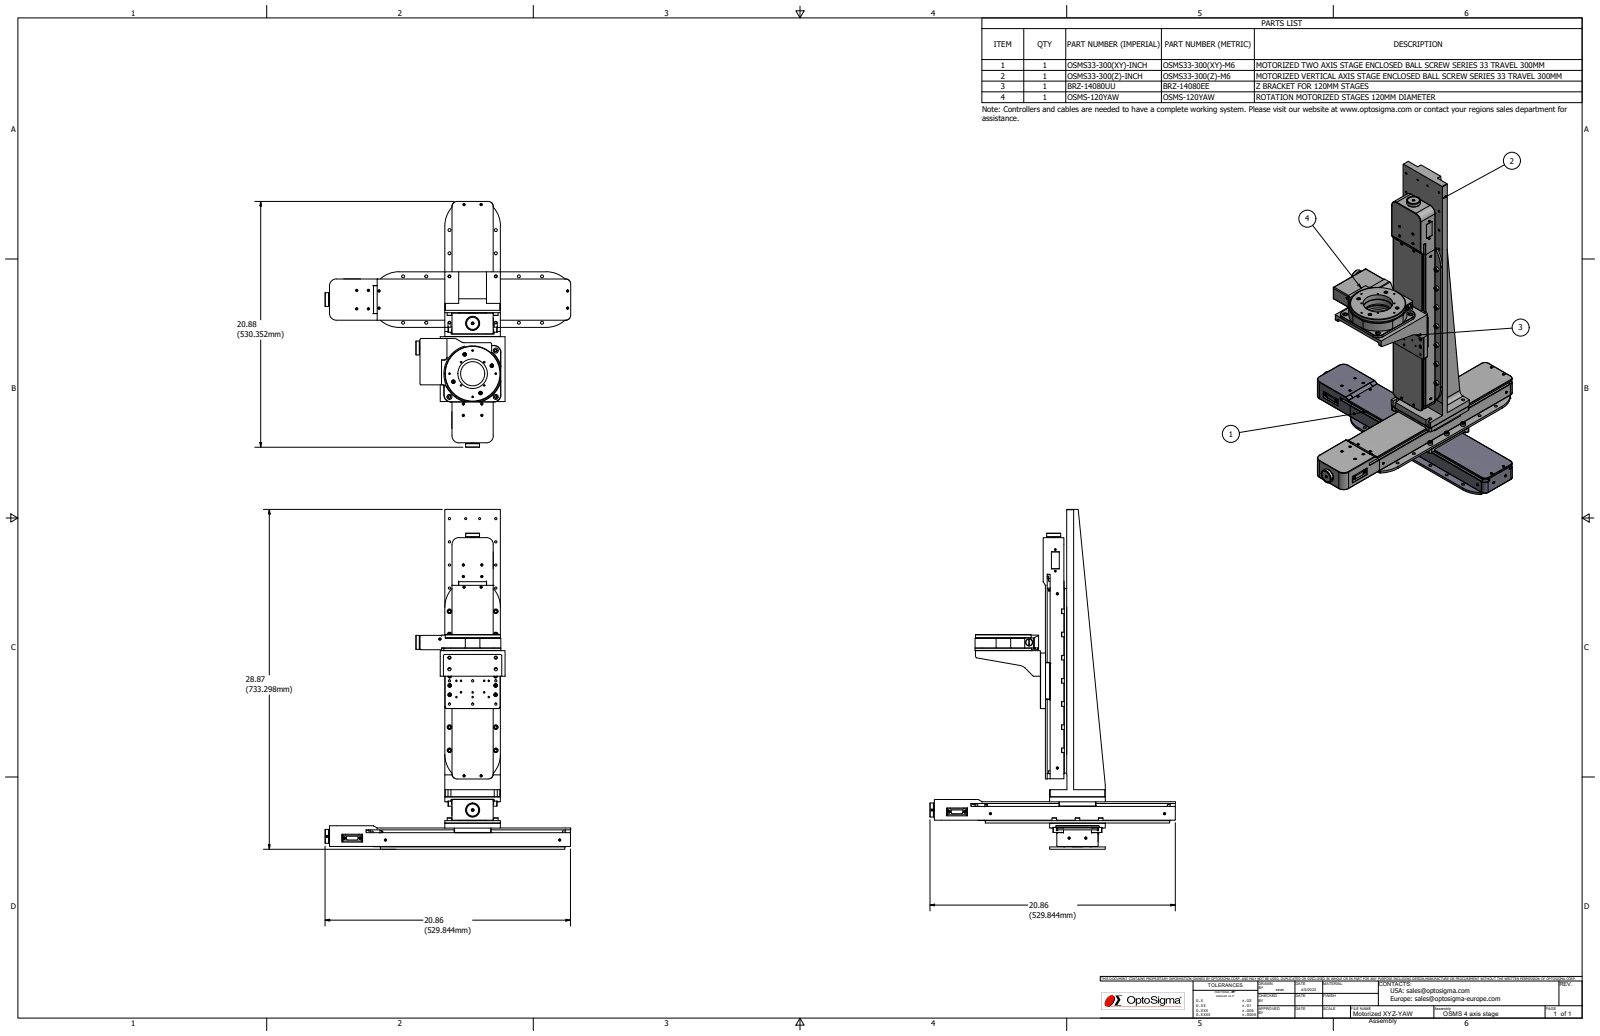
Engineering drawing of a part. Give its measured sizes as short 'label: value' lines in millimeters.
name: Motorized XYZ-YAW Assembly; OSMS33-300(XY)_STP; OSMS33-300(Z)_STP; ZBR-14080EE (+1 more)
written by: Autodesk Inventor 2022 (AUTOMOTIVE_DESIGN)
unit: mm
bodies: 13 solids, 10131 faces (6395 planar, 2373 cylindrical, 1363 other)
size: 733.4 × 530.3 × 530.3
volume: 6 832 000 mm³; area: 2 120 000 mm²
holes: 88× ⌀3.24, 83× ⌀6.5, 65× ⌀2.11, 48× ⌀4.5, 46× ⌀3.5, 41× ⌀2.46, 37× ⌀8, 36× ⌀4.13, 32× ⌀5.5, 32× ⌀9.5, 31× ⌀1.57, 27× ⌀2.11
bosses: 85× ⌀4, 59× ⌀3, 56× ⌀5.5, 49× ⌀7, 46× ⌀3.2, 33× ⌀5, 32× ⌀8.5, 20× ⌀10
rounds: 243× R0.5, 67× R1, 65× R3, 26× R5, 25× R4, 24× R0.25, 24× R0.7, 16× R3.5
face distances: 56.7, 1, 40, 0.8, 46, 45, 50.7, 88.2, 5, 41
hole spacings: 100, 105.95, 50, 61.03, 82.01, 111.8, 119.27, 141.42
